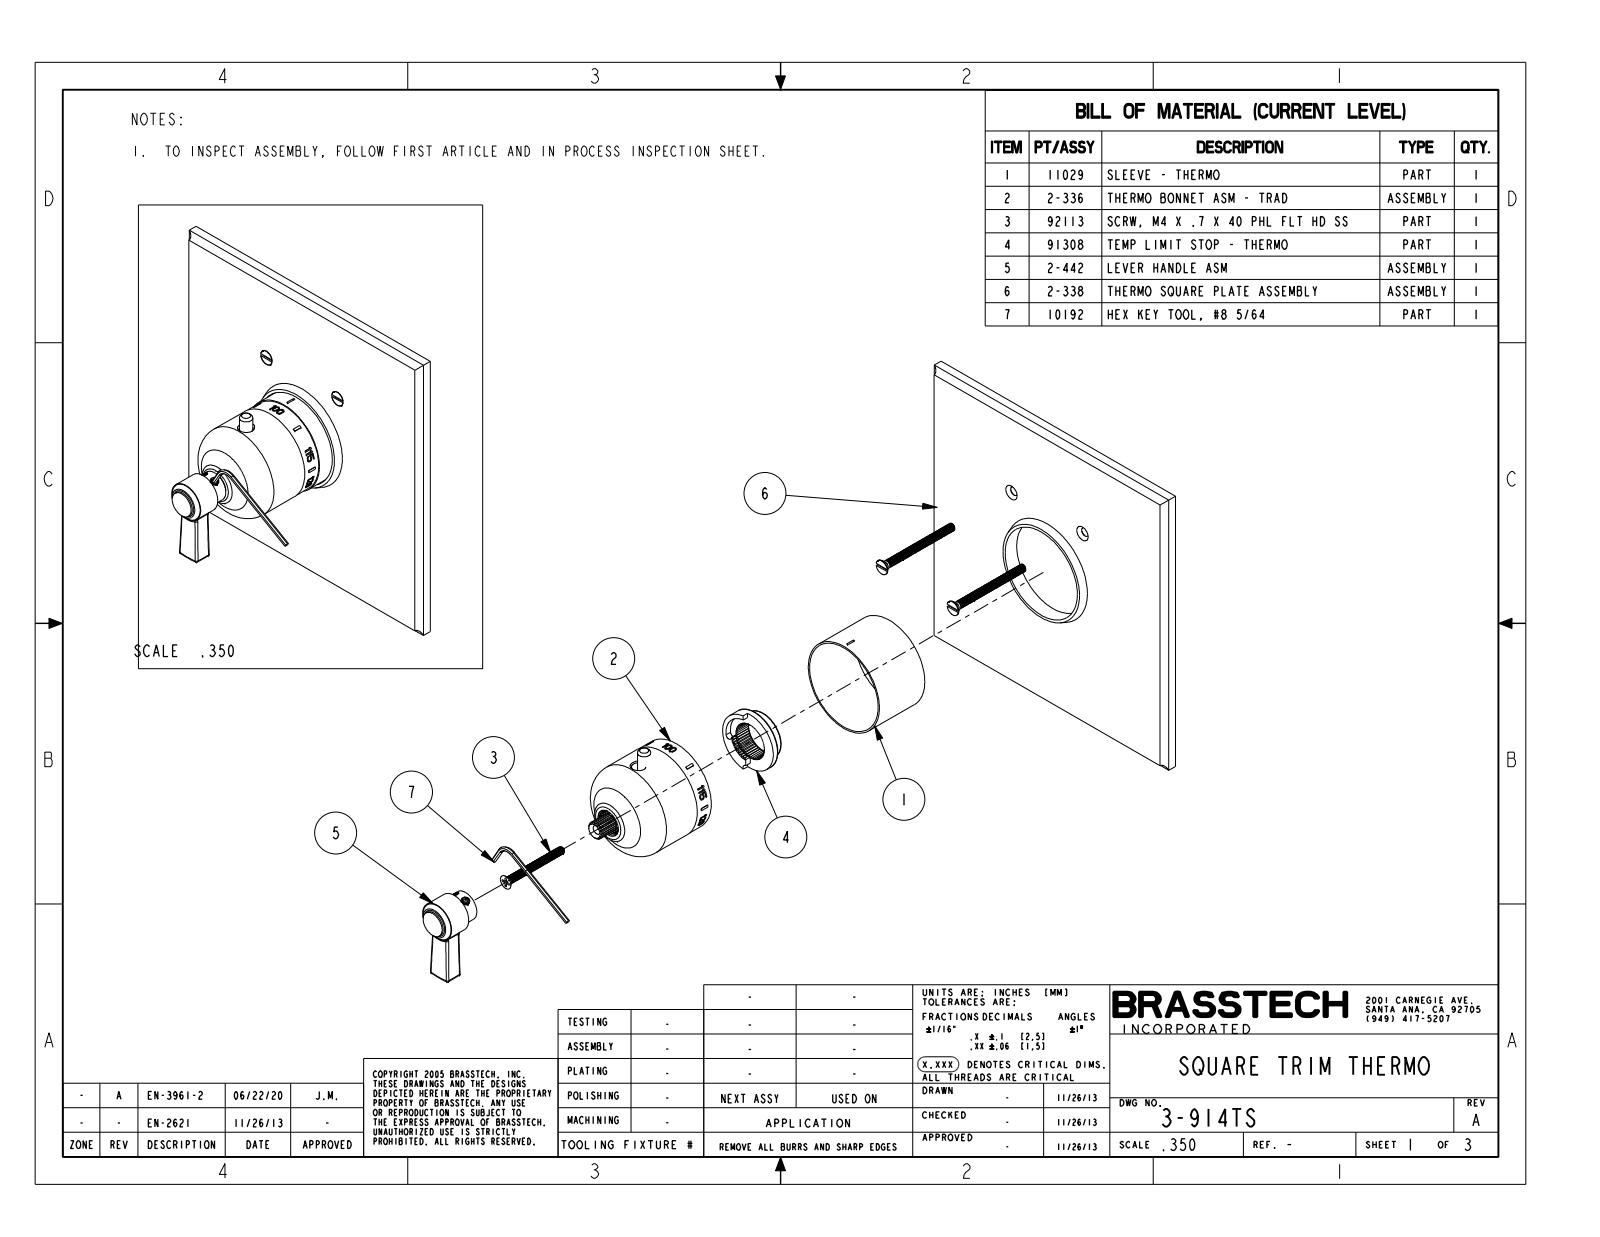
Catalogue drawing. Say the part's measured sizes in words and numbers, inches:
The part is named "3-914TS". Its 3-D file was written by "CREO PARAMETRIC BY PTC INC, 2018400 (CONFIG_CONTROL_DESIGN)". It is 1 solid with 425 faces: 338 planar, 45 cylindrical and 42 other. Overall it measures 6.5 by 6.5 by 3.648 inches. Its volume is 19.86 cubic inches and its surface area 108.2 square inches. Round bosses or shafts: 1 of diameter 1.97, 1 of diameter 1.94, 1 of diameter 1.929, 1 of diameter 0.8, 1 of diameter 0.625, 1 of diameter 0.525, 1 of diameter 0.37, 1 of diameter 0.26. Partial cylindrical surfaces (rounded edges, fillets, slot ends): 4 of radius 0.125, 2 of radius 0.04, 2 of radius 0.055, 1 of radius 0.969. The main face-to-face distances are 0.313, 6.5, 2.735, 2.706, 2.393, 3.648, 3.335, 0.943, 2.422, 0.03.
